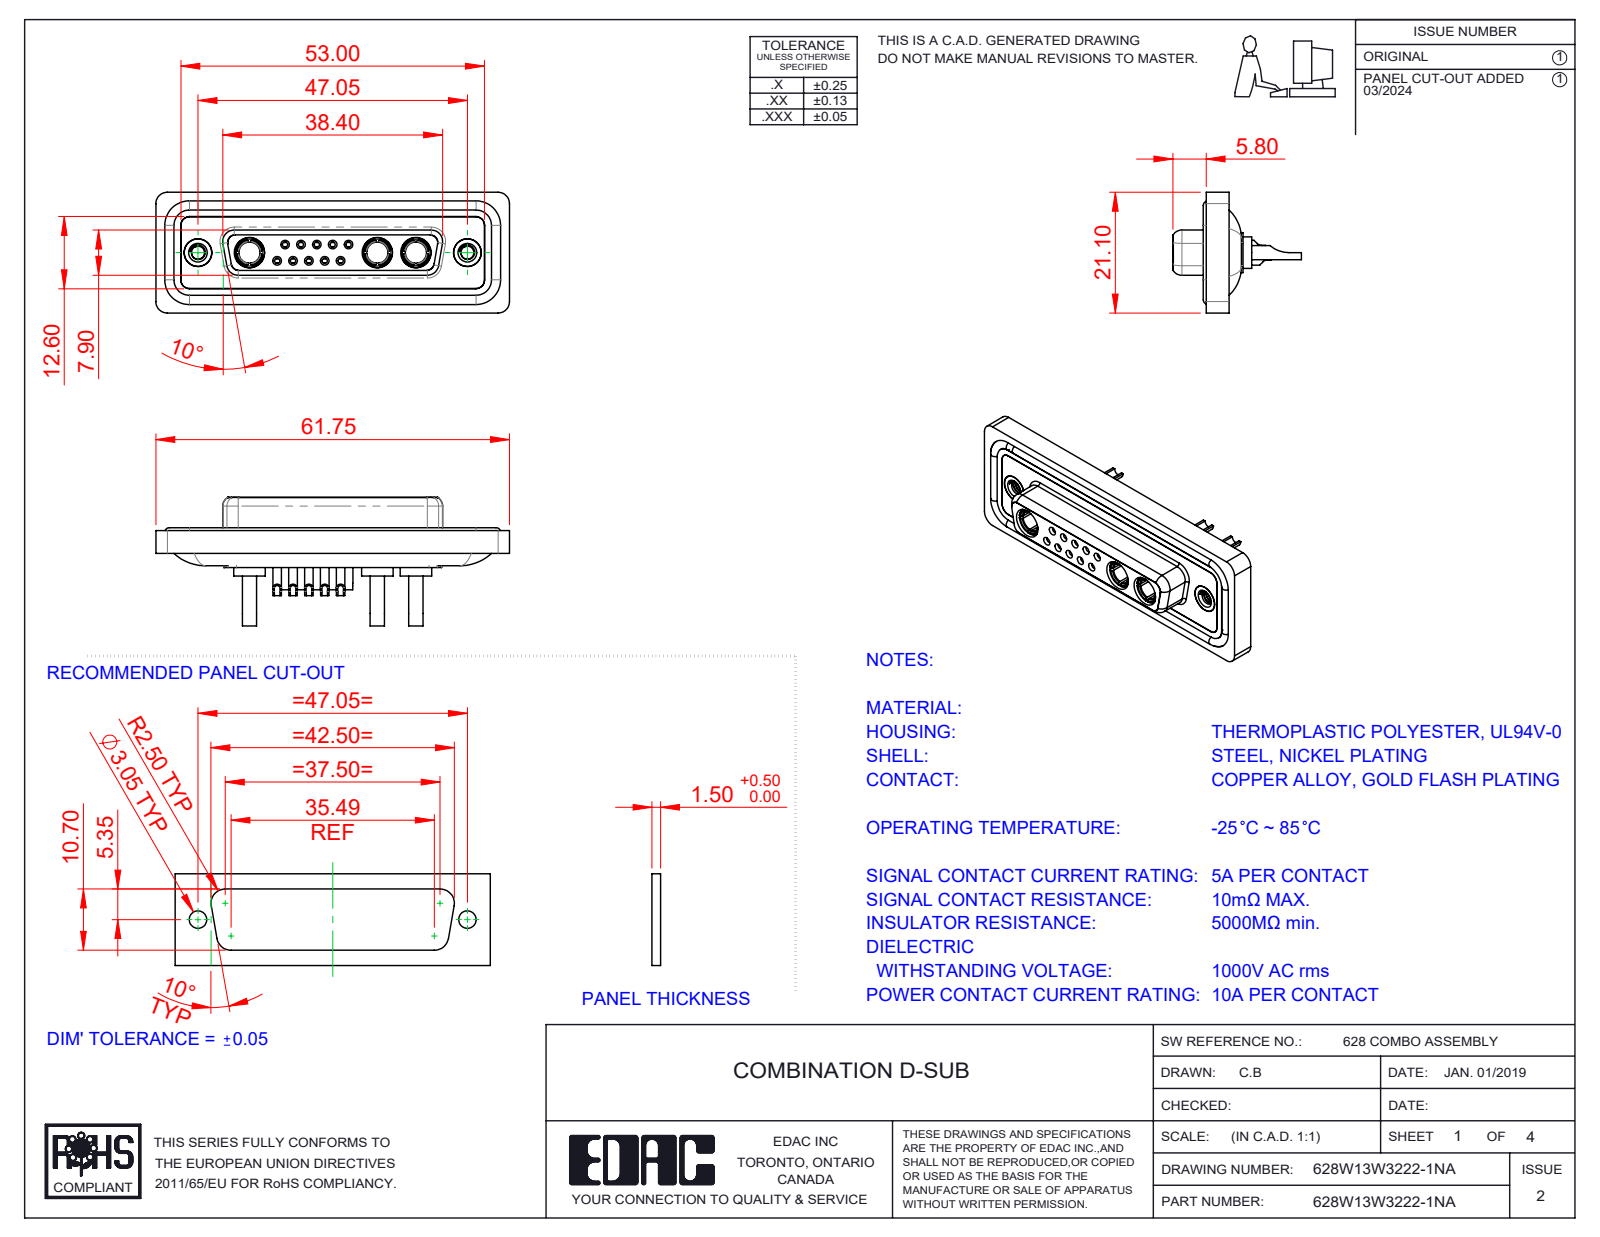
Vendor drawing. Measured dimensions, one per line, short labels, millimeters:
name: 628W13W3222-1NA; 628Combo Threaded Rivet_A; Power Socket_10A SC; 628Combo Contact Row 2_22 (+5 more)
written by: SolidWorks 2023 (CONFIG_CONTROL_DESIGN)
unit: mm
bodies: 23 solids, 1171 faces (368 planar, 478 cylindrical, 325 other)
size: 61.75 × 22.45 × 21.1
volume: 8 287 mm³; area: 13 954 mm²
holes: 10× ⌀0.9, 10× ⌀1, 10× ⌀1.1, 10× ⌀1.5, 10× ⌀2, 5× ⌀1.6, 5× ⌀1.7, 5× ⌀4.85, 3× ⌀1.7, 3× ⌀3.7, 3× ⌀5.3, 2× ⌀2.26
bosses: 10× ⌀2.2, 9× ⌀1.6, 3× ⌀5.5, 3× ⌀5.2, 3× ⌀4.96, 3× ⌀4.75, 3× ⌀3.75, 3× ⌀2.5
rounds: 22× R1.5, 18× R2, 8× R1.35, 8× R1.6, 6× R1, 4× R0.25, 4× R0.5, 4× R0.6
face distances: 0.4, 1.8, 7.45, 5.65, 0.5, 6.6, 7.05, 1.6, 2.9, 1.1
hole spacings: 3.16, 2.77, 5.03, 5.04, 5.54, 8.31, 7.49, 2.76
